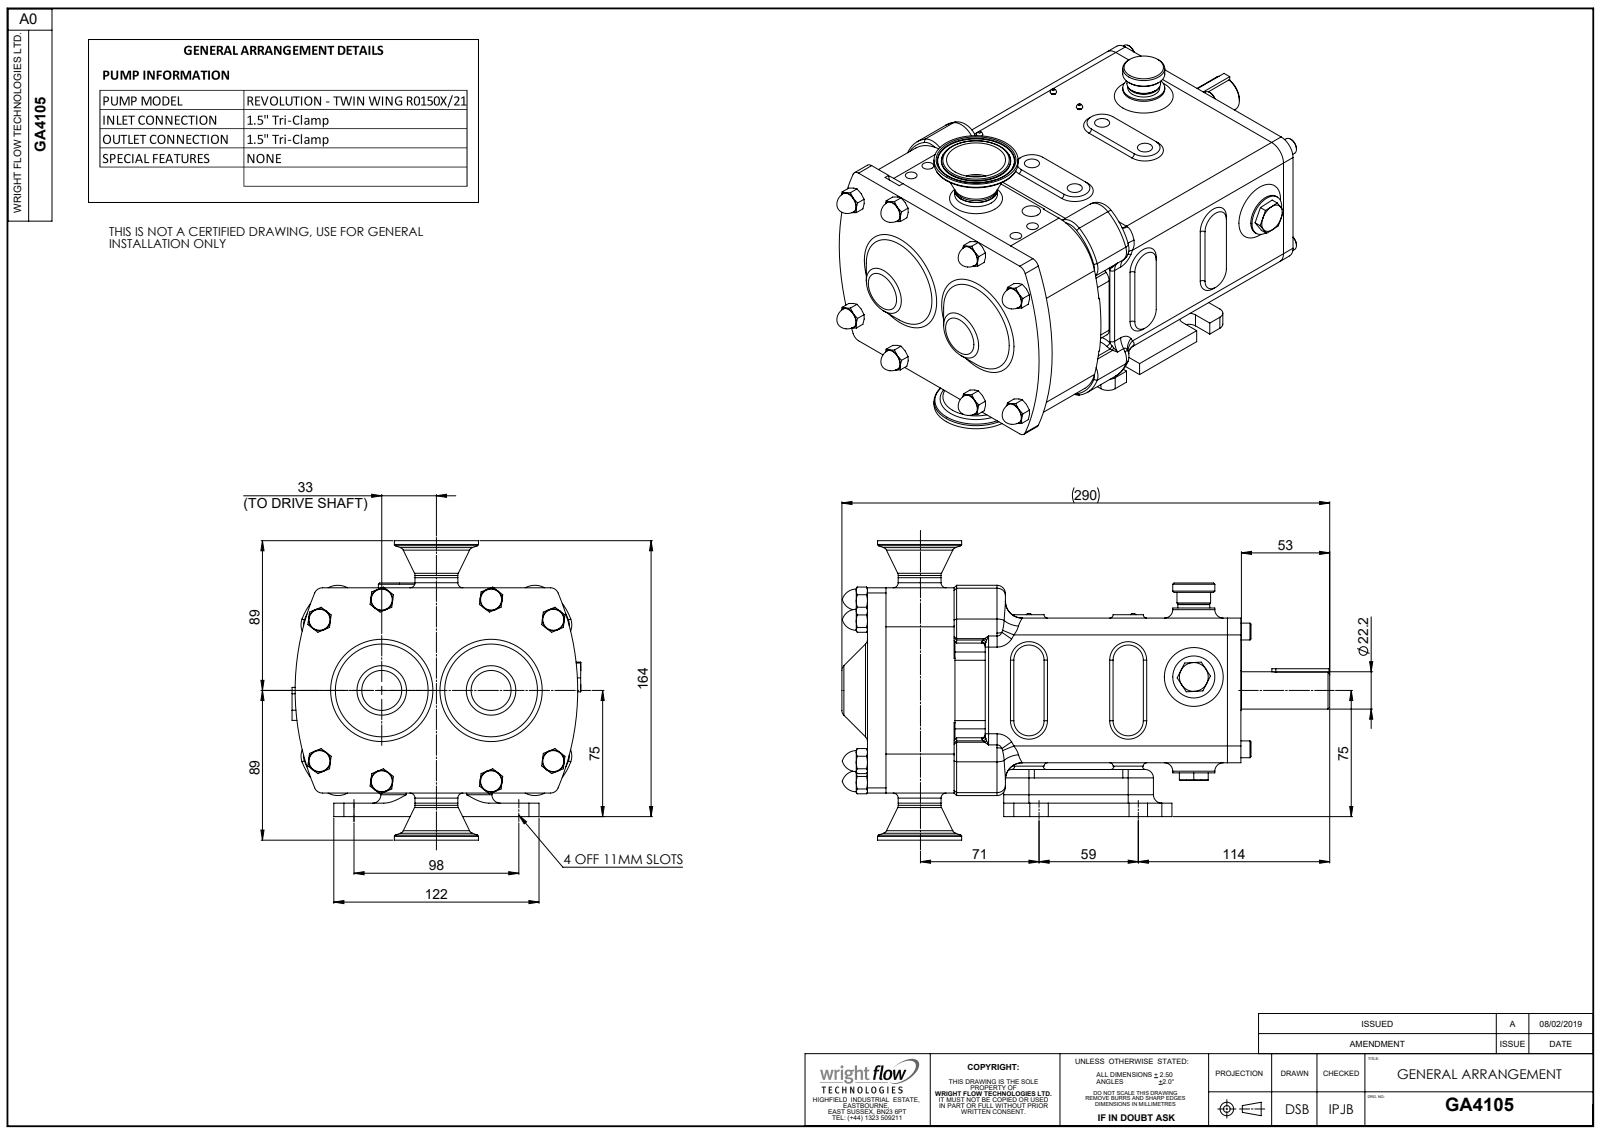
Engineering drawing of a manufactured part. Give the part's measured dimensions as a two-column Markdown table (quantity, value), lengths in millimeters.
| quantity | value |
| --- | --- |
| part name | Copy of R0150 CPP V LHD^GA4105; GA4105; Copy of Rev 1.5 Inch to 1 Inch Tri-Clamp^GA4105 |
| STEP written by | SolidWorks 2023 (AUTOMOTIVE_DESIGN) |
| units | millimeters |
| bodies | 3 solids, 1232 faces (360 planar, 301 cylindrical, 571 other) |
| overall size | 290 × 178 × 171.64 |
| volume | 3 472 000 mm³ |
| surface area | 231 510 mm² |
| round holes (diameter × count) | 7 × 4, 9 × 4, 11 × 2, 22.2 × 1, 22.53 × 1 |
| round bosses / shafts (diameter × count) | 10 × 6, 25 × 4, 13 × 4, 50 × 1, 25.5 × 1, 25.4 × 1, 25.02 × 1, 22.2 × 1 |
| partial cylindrical surfaces (radius × count) | 2 × 28, 10 × 26, 5 × 19, 6 × 14, 8 × 8, 31 × 6, 1.25 × 4, 5.5 × 4 |
| main face-to-face distances | 86, 6, 222, 14, 18, 104, 8, 2, 118, 151 |
| hole center spacings | 14, 15.57, 27.06, 35.39, 36, 44.14, 45.24, 53.02 |
